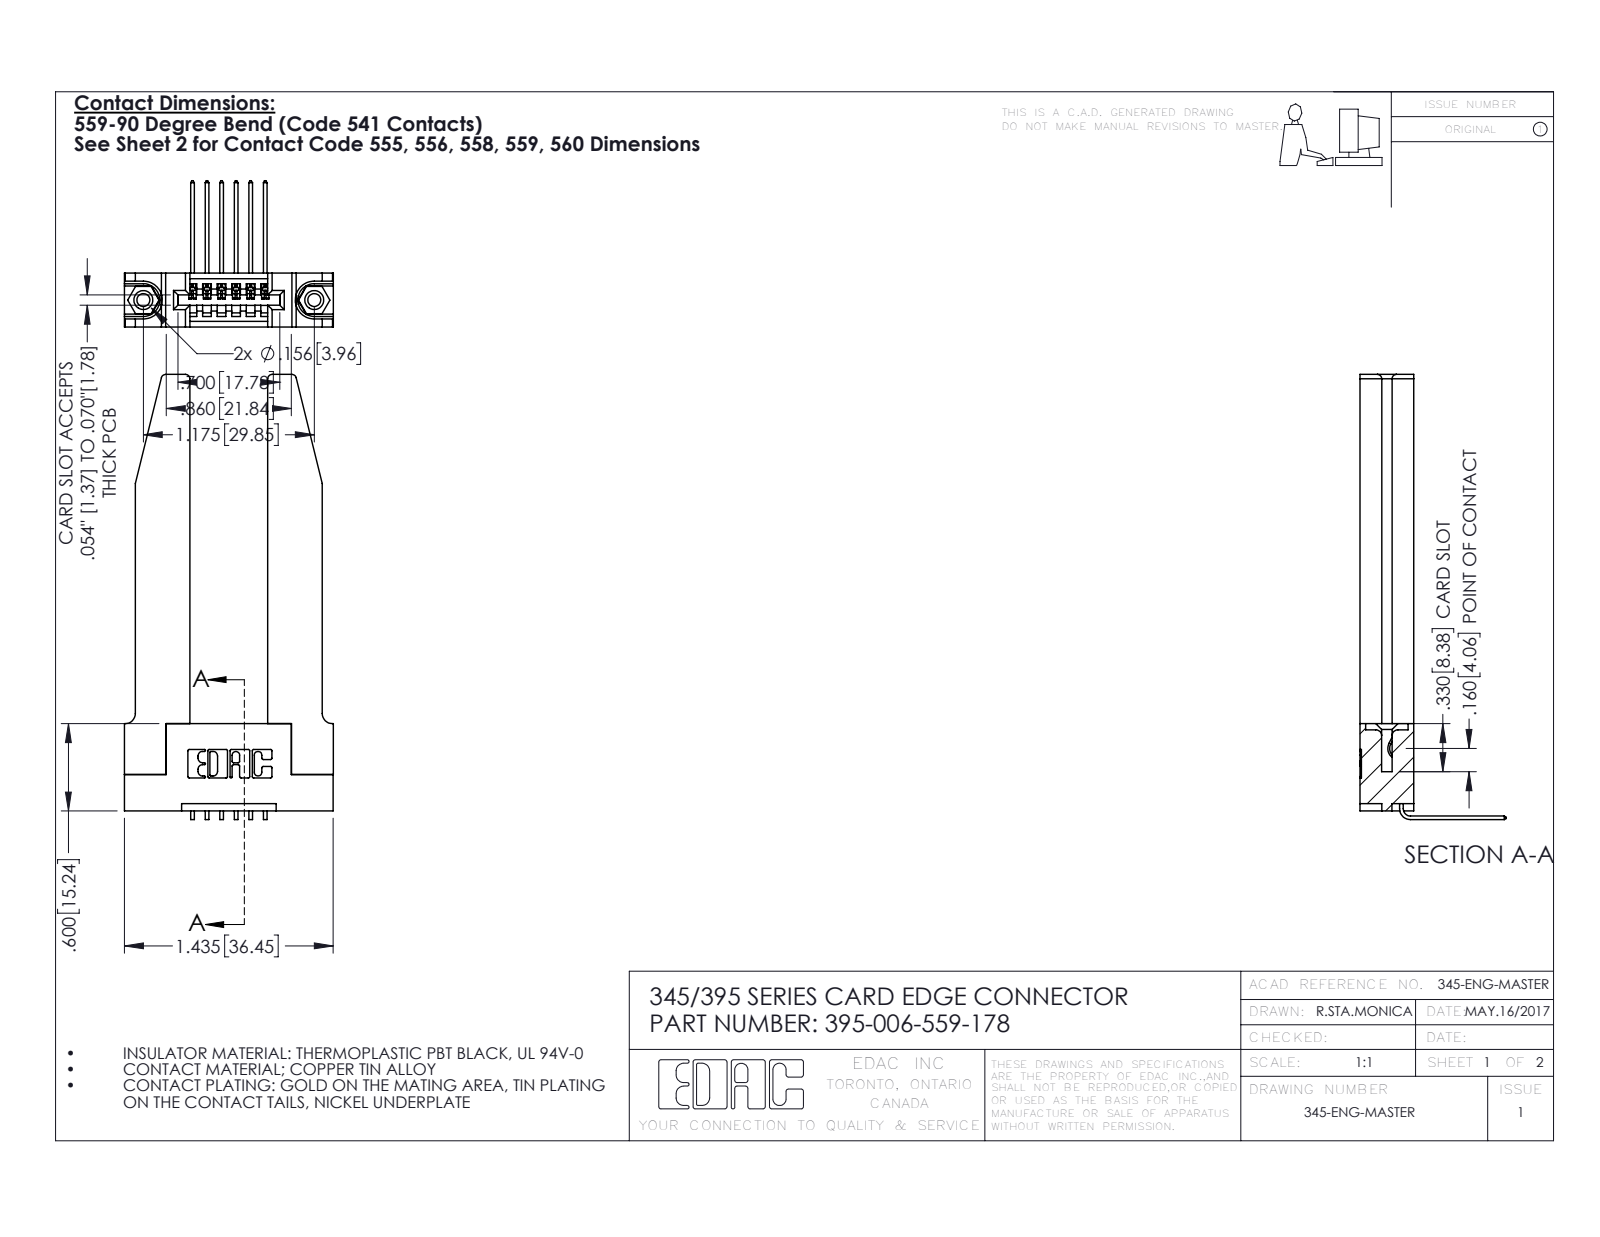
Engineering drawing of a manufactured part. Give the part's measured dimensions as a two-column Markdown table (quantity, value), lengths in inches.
| quantity | value |
| --- | --- |
| part name | 345 Part_Flush Mounting Lugs - 0.156 Dia-TH; 345-292-001_558 559 Tail - 1; 345-250-001_345-250-001-102; 395-006-559-178 (+1 more) |
| STEP written by | SolidWorks 2016 (CONFIG_CONTROL_DESIGN) |
| units | inches |
| bodies | 11 solids, 720 faces (474 planar, 194 cylindrical, 52 other) |
| overall size | 3.059 × 1.436 × 1.005 |
| volume | 0.669 in³ |
| surface area | 16.6 in² |
| round holes (diameter × count) | 0.089 × 2, 0.125 × 2, 0.156 × 2, 0.064 × 1 |
| round bosses / shafts (diameter × count) | 0.155 × 2 |
| partial cylindrical surfaces (radius × count) | 0.01 × 22, 0.006 × 12, 0.03 × 8, 0.007 × 6, 0.031 × 6, 0.026 × 3, 0.031 × 2, 0.04 × 2 |
| main face-to-face distances | 0.37, 0.15, 0.22, 0.535, 0.072, 0.148, 0.077, 0.298, 0.2, 0.095 |
| hole center spacings | 0.27, 0.946, 1.175 |
